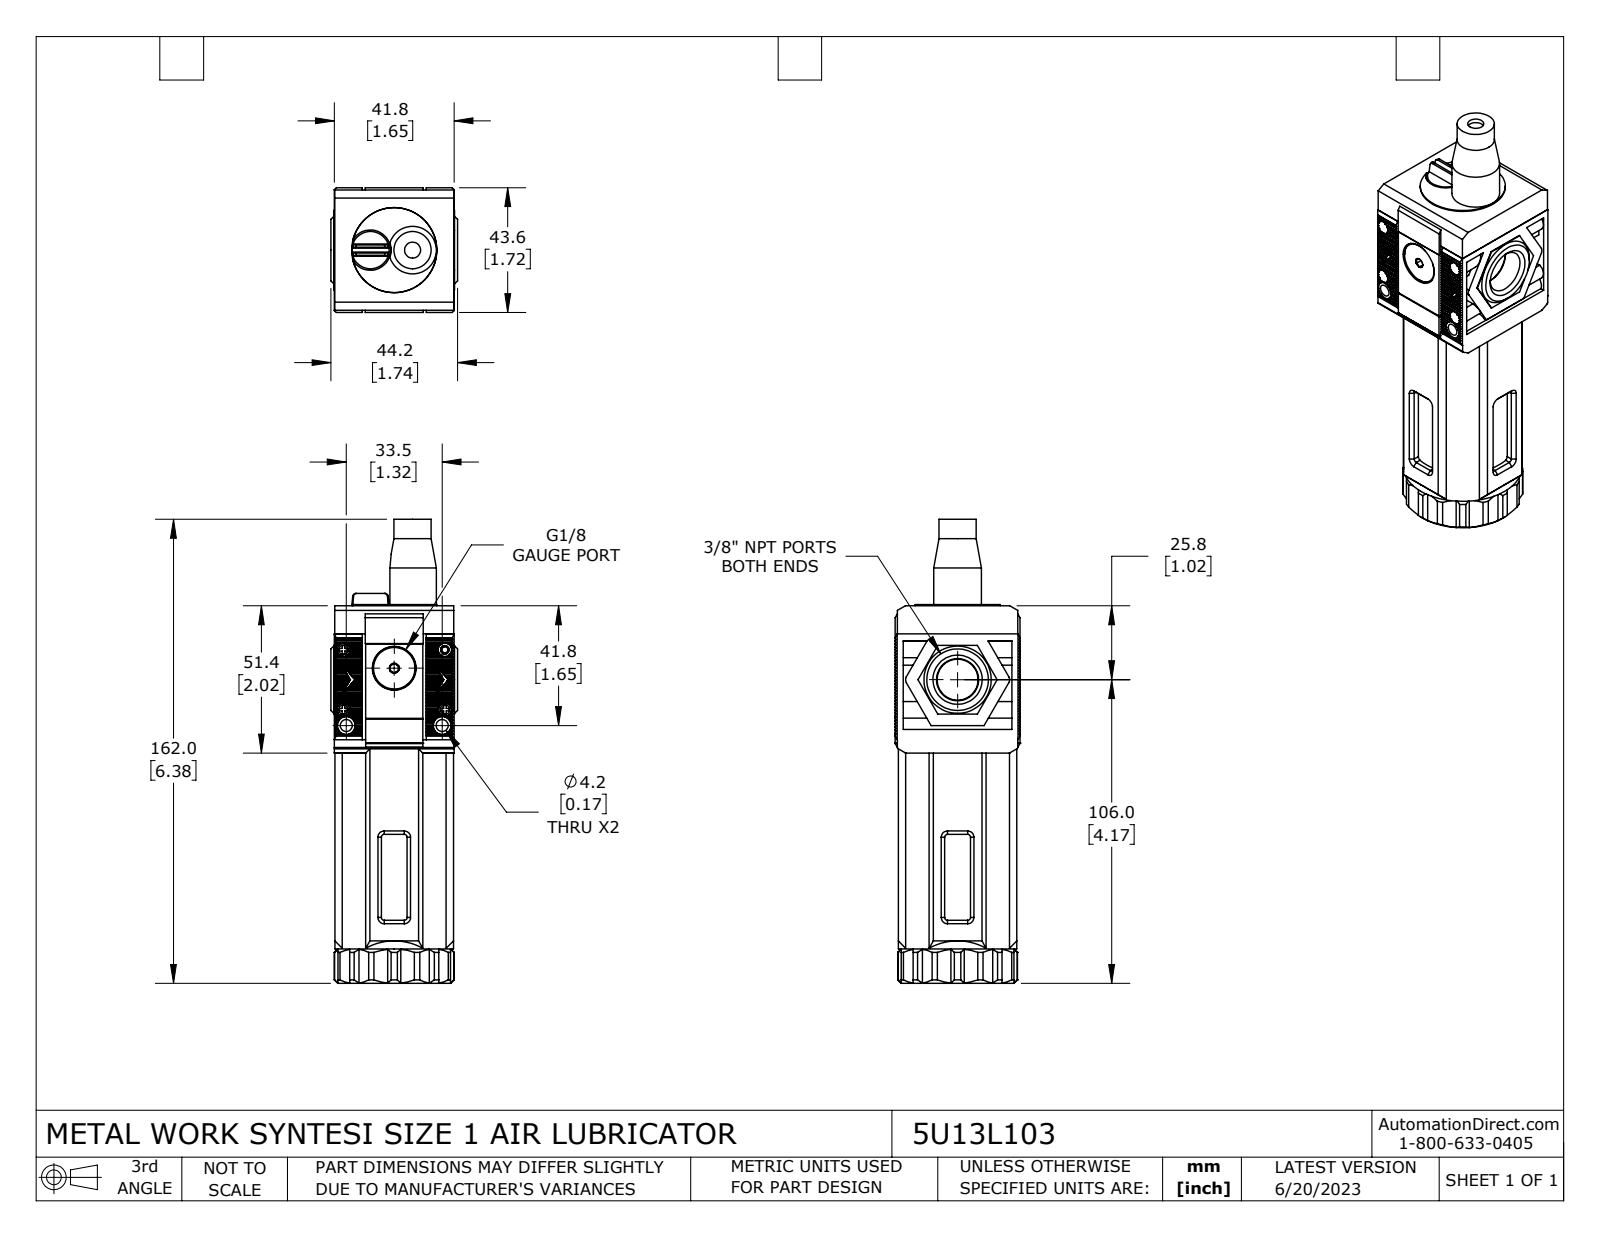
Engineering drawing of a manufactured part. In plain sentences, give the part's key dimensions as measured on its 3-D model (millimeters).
The part is named "5U13L103". Its 3-D file was written by "SolidWorks 2021 (CONFIG_CONTROL_DESIGN)". It is 13 solids with 1313 faces: 905 planar, 258 cylindrical and 150 other. Overall it measures 162 by 44.2 by 43.6 millimeters. Its volume is 134 300 cubic millimeters and its surface area 65 100 square millimeters. Round holes: 4 of diameter 2.1, 4 of diameter 3, 4 of diameter 4.7, 2 of diameter 4.2, 1 of diameter 5.6, 1 of diameter 8.6, 1 of diameter 14.1, 1 of diameter 15.3, 1 of diameter 29.7, 1 of diameter 30, 1 of diameter 31.3, 1 of diameter 34. Round bosses or shafts: 3 of diameter 4.6, 3 of diameter 2.6, 2 of diameter 13, 2 of diameter 6.2, 1 of diameter 41.4, 1 of diameter 35.6, 1 of diameter 25, 1 of diameter 22.8. Partial cylindrical surfaces (rounded edges, fillets, slot ends): 8 of radius 1, 4 of radius 0.6, 4 of radius 3.1, 2 of radius 0.2, 2 of radius 2, 1 of radius 7.2, 1 of radius 11, 1 of radius 20.9. The main face-to-face distances are 41.4, 41.6, 1.1, 42.5, 40, 7.6, 41.7, 33.8, 34, 7.8. The hole center spacings are 5.6, 18.8, 20.9, 22.9, 26.1, 26.5, 34.9, 35.4.
